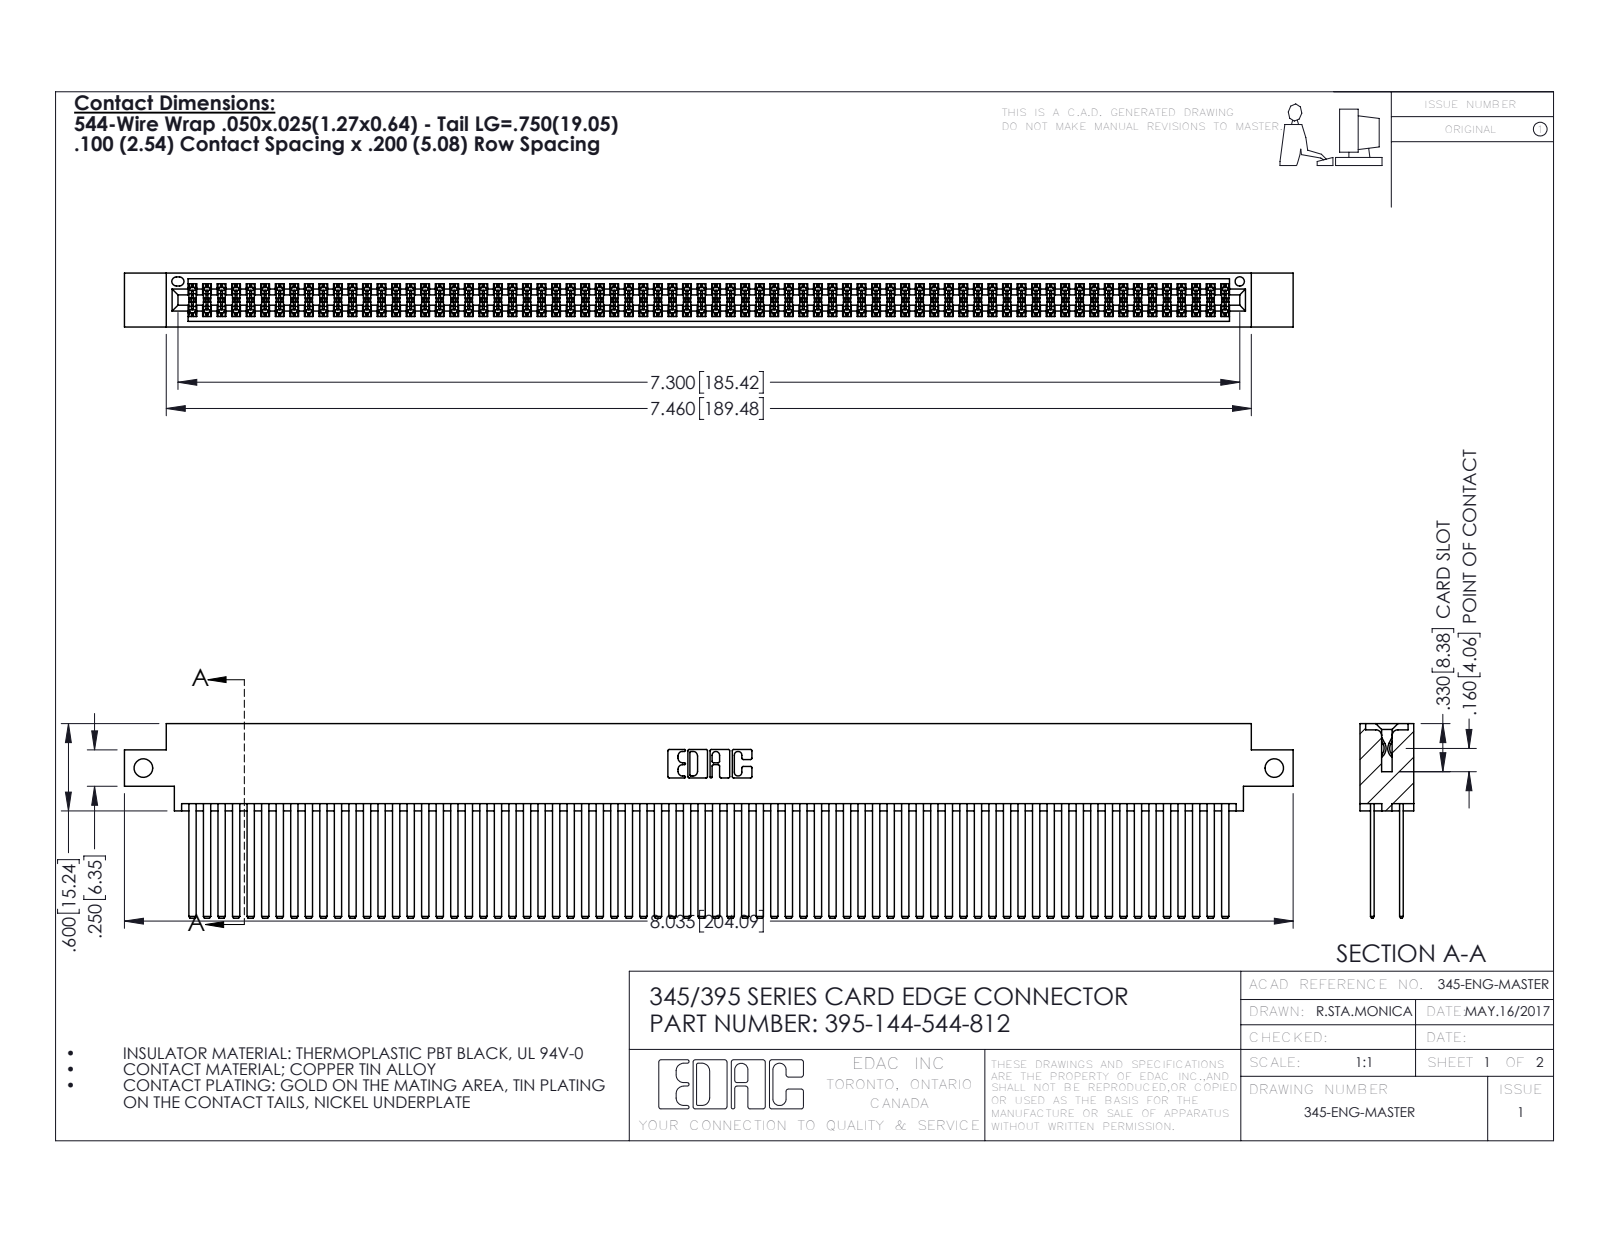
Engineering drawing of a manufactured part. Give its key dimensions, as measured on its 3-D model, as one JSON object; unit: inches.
{"part_name": "345 Part_0.170 Offset - Side Mount; 395-144-544-812; 345-292-001_345-293-144", "step_written_by": "SolidWorks 2016 (CONFIG_CONTROL_DESIGN)", "units": "inches", "bodies": {"solids": 145, "faces": 6466, "planar": 4260, "cylindrical": 2206, "other": 0}, "overall_size": [8.035, 1.337, 0.37], "volume_in3": 1.338, "surface_area_in2": 60.31, "round_holes": [[0.128, 2], [0.064, 1]], "partial_cylinders_radius": [[0.006, 216], [0.01, 22], [0.007, 6], [0.031, 6], [0.026, 3], [0.014, 2], [0.019, 2], [0.022, 2]], "face_to_face_distances": [0.2, 0.025, 0.298, 0.072, 0.098, 0.272, 0.225, 0.175, 0.37, 0.15], "hole_center_spacings": [7.775]}
